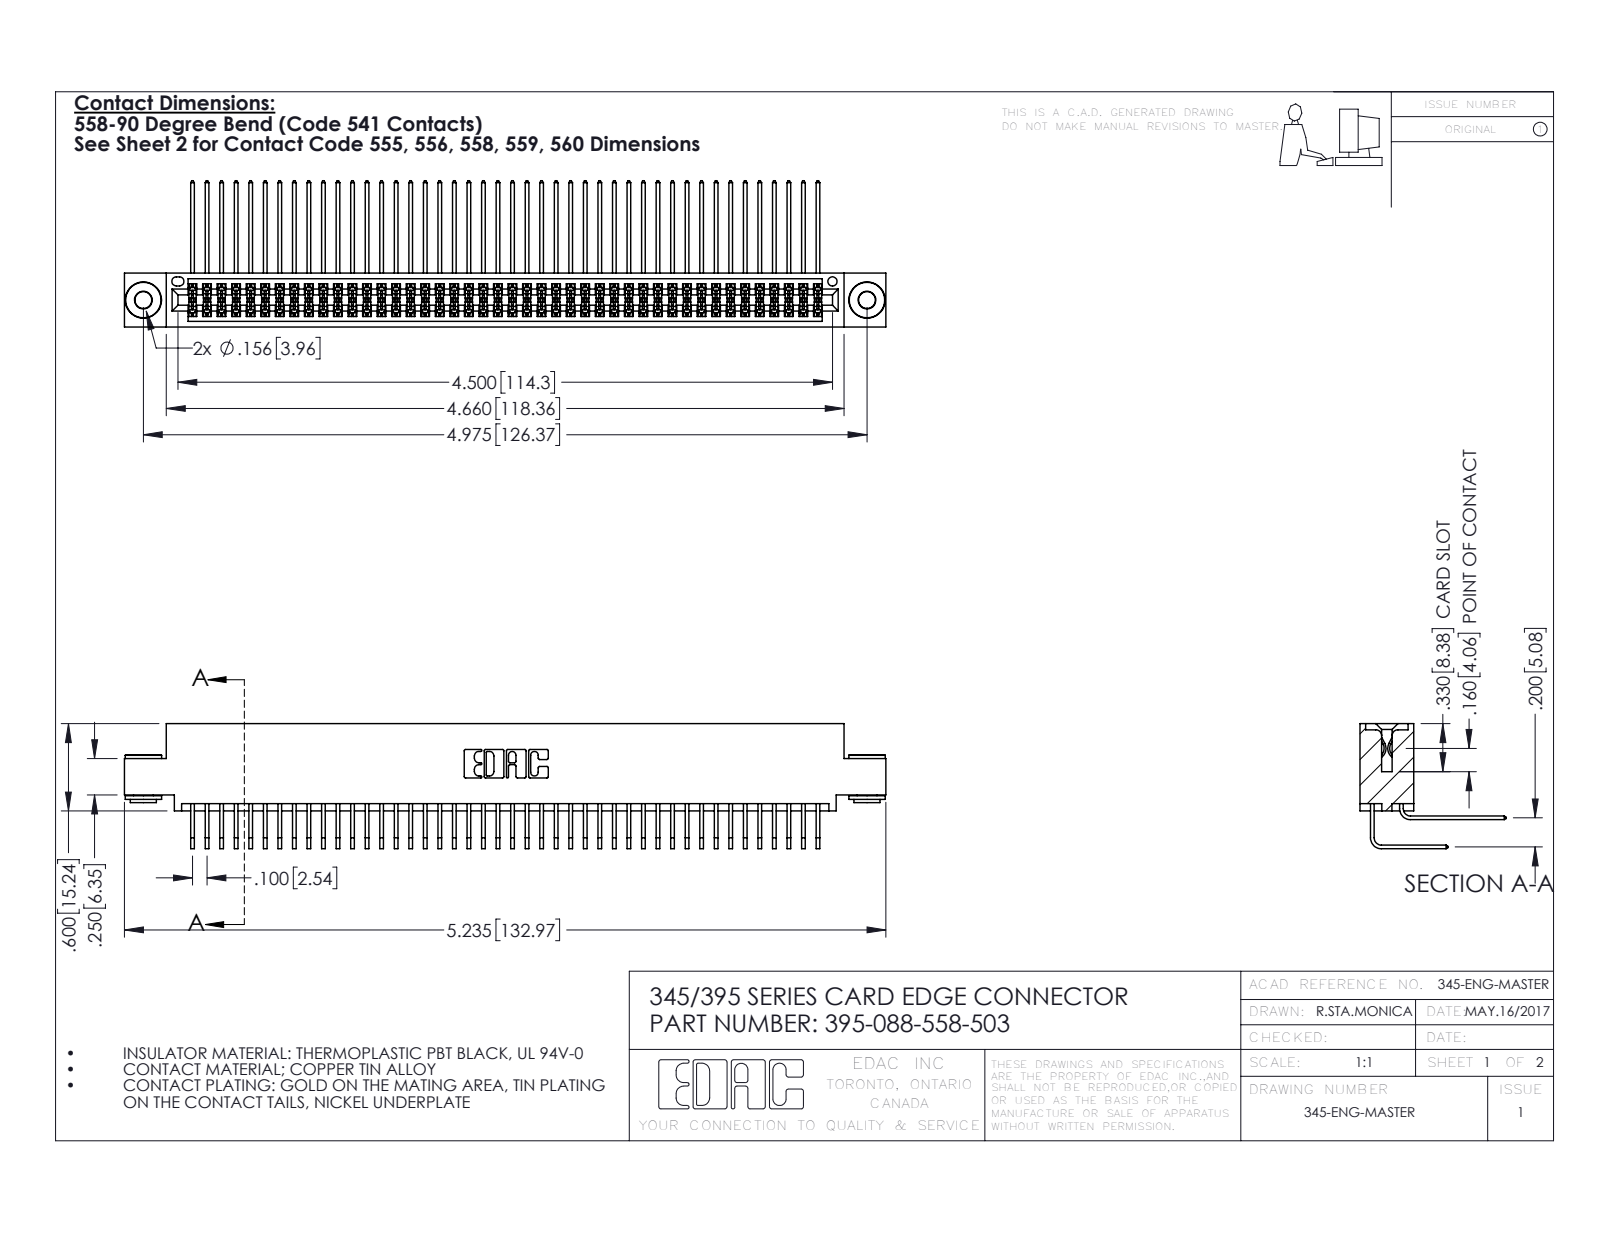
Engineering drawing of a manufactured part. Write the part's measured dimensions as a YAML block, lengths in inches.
part_name: "345-292-001_558 559 Tail - 1; 345-250-002_345-250-002-102; 345-292-001_558 Tail - 2; 345 Part_0.110 Offset - 0.156 Dia-TH (+1 more)"
step_written_by: "SolidWorks 2016 (CONFIG_CONTROL_DESIGN)"
units: inches
bodies: {solids: 91, faces: 4744, planar: 3174, cylindrical: 1562, other: 8}
overall_size: [5.235, 1.005, 0.859]
volume: 0.817
surface_area: 34.9
round_holes:
  - {diameter: 0.116, count: 2}
  - {diameter: 0.156, count: 2}
  - {diameter: 0.064, count: 1}
round_bosses_or_shafts:
  - {diameter: 0.25, count: 2}
  - {diameter: 0.18, count: 2}
  - {diameter: 0.136, count: 2}
partial_cylinders:
  - {radius: 0.006, count: 133}
  - {radius: 0.01, count: 22}
  - {radius: 0.007, count: 6}
  - {radius: 0.031, count: 6}
  - {radius: 0.026, count: 3}
  - {radius: 0.014, count: 2}
  - {radius: 0.019, count: 2}
  - {radius: 0.022, count: 2}
face_to_face_distances: [0.072, 0.298, 0.2, 0.37, 0.025, 0.098, 0.272, 0.225, 0.025, 0.175]
hole_center_spacings: [0.27, 4.739, 4.975]
